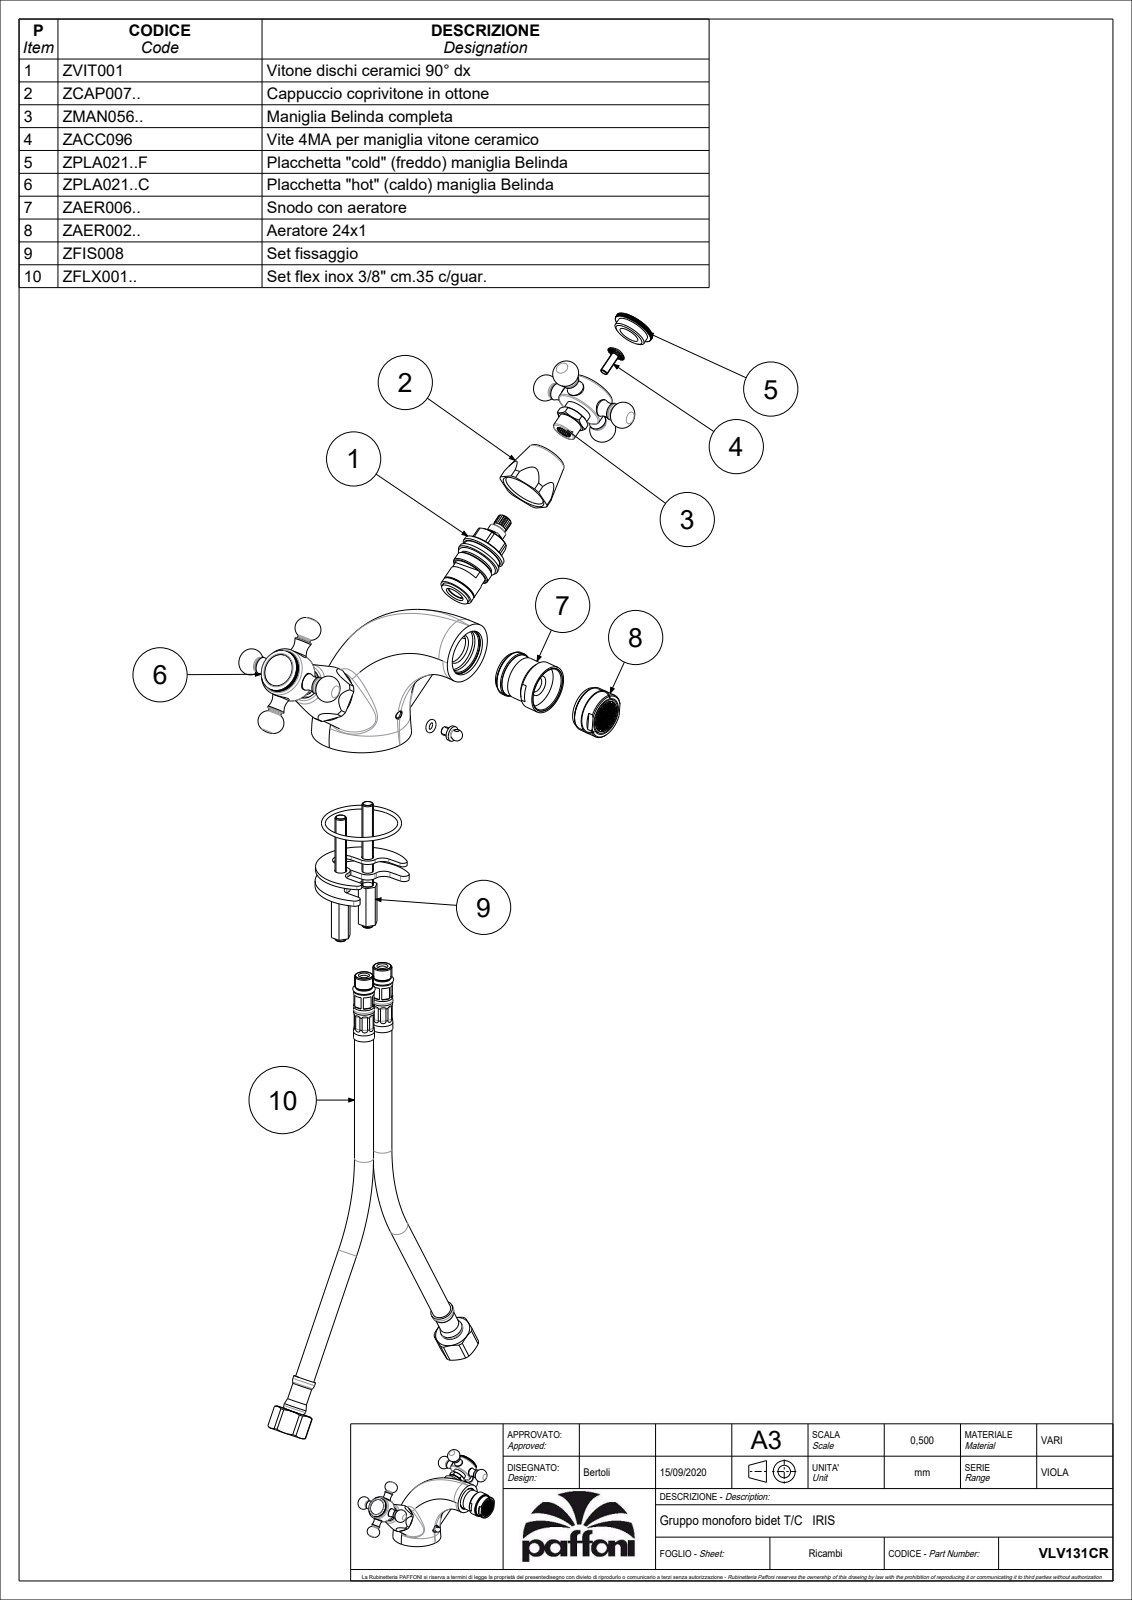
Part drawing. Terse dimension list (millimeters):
name: VLV131CR
written by: CREO PARAMETRIC BY PTC INC, 2020044 (CONFIG_CONTROL_DESIGN)
unit: mm
bodies: 1 solid, 1021 faces (494 planar, 320 cylindrical, 207 other)
size: 180.18 × 128.34 × 87.28
volume: 222 817 mm³; area: 42 969 mm²
holes: 2× ⌀5.5, 2× ⌀7.75, 2× ⌀8, 2× ⌀9, 2× ⌀11, 2× ⌀18.6, 2× ⌀21.5, 1× ⌀42.5
bosses: 6× ⌀9, 6× ⌀7, 2× ⌀27.5, 2× ⌀25, 2× ⌀14, 2× ⌀13, 1× ⌀37.5, 1× ⌀25.8
rounds: 2× R11, 2× R14.5
face distances: 35.32, 26.5, 21.88, 57.2, 28.7, 3, 25.7, 46, 24.12, 11.2
hole spacings: 10.97, 12.08, 13.46, 22.61, 15, 22
